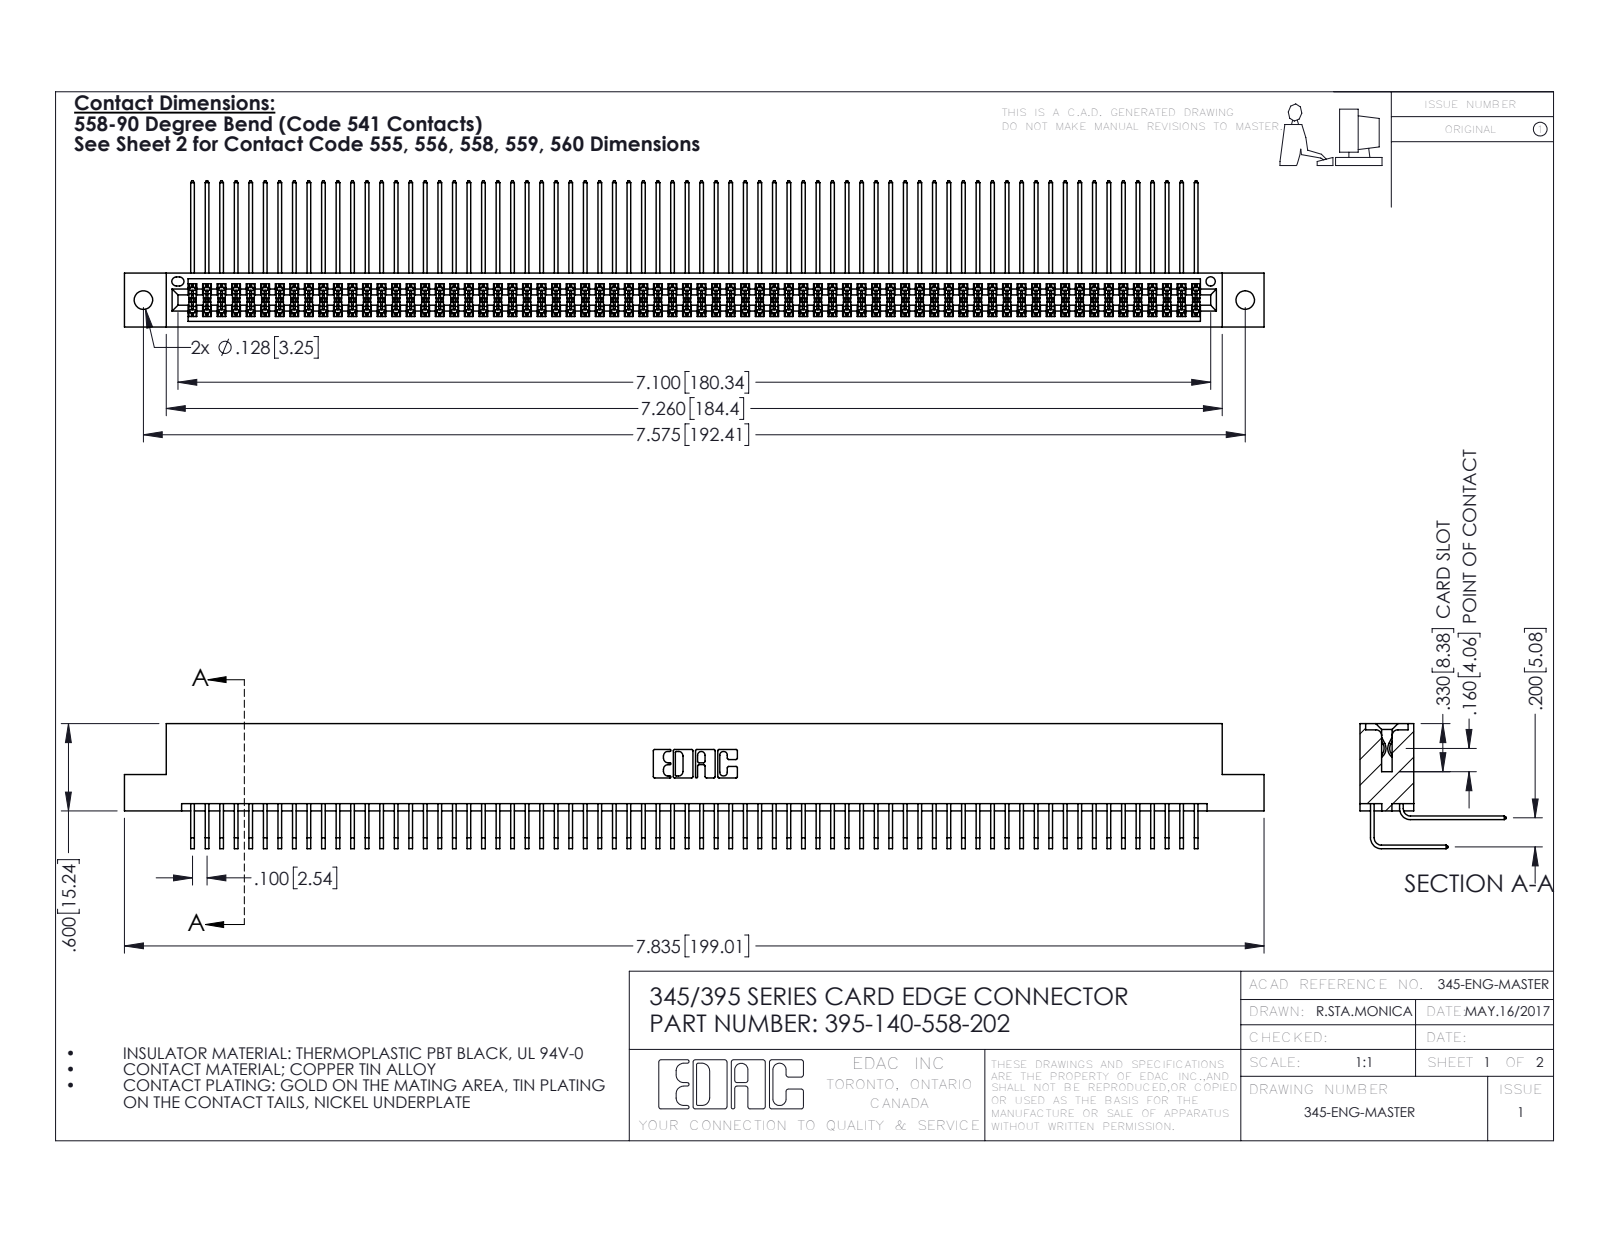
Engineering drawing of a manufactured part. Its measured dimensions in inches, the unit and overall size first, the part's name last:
Units: inches
Overall size (bounding box): 7.835 × 1.005 × 0.859
Round holes (diameter × count): ⌀0.128 ×2, ⌀0.064 ×1
Partial cylindrical surfaces — rounded edges, fillets, slot ends (radius × count): R0.006 ×279, R0.01 ×22, R0.007 ×6, R0.031 ×6, R0.026 ×3, R0.014 ×2, R0.019 ×2, R0.022 ×2
Main face-to-face distances: 0.072, 0.298, 0.2, 0.37, 0.098, 0.272, 0.025, 0.225, 0.025, 0.175
Hole centre spacings: 0.27, 7.339, 7.575
Volume: 1.243 in³ · Surface area: 52.96 in²
Bodies: 141 solids, 7406 faces (4980 planar, 2426 cylindrical, 0 other)
Part name (STEP PRODUCT): 395-140-558-202; 345-292-001_558 Tail - 2; 345-292-001_558 559 Tail - 1; 345 Part_Flush Mounting Lugs - 0.128 Dia
STEP written by: SolidWorks 2016 (CONFIG_CONTROL_DESIGN)
